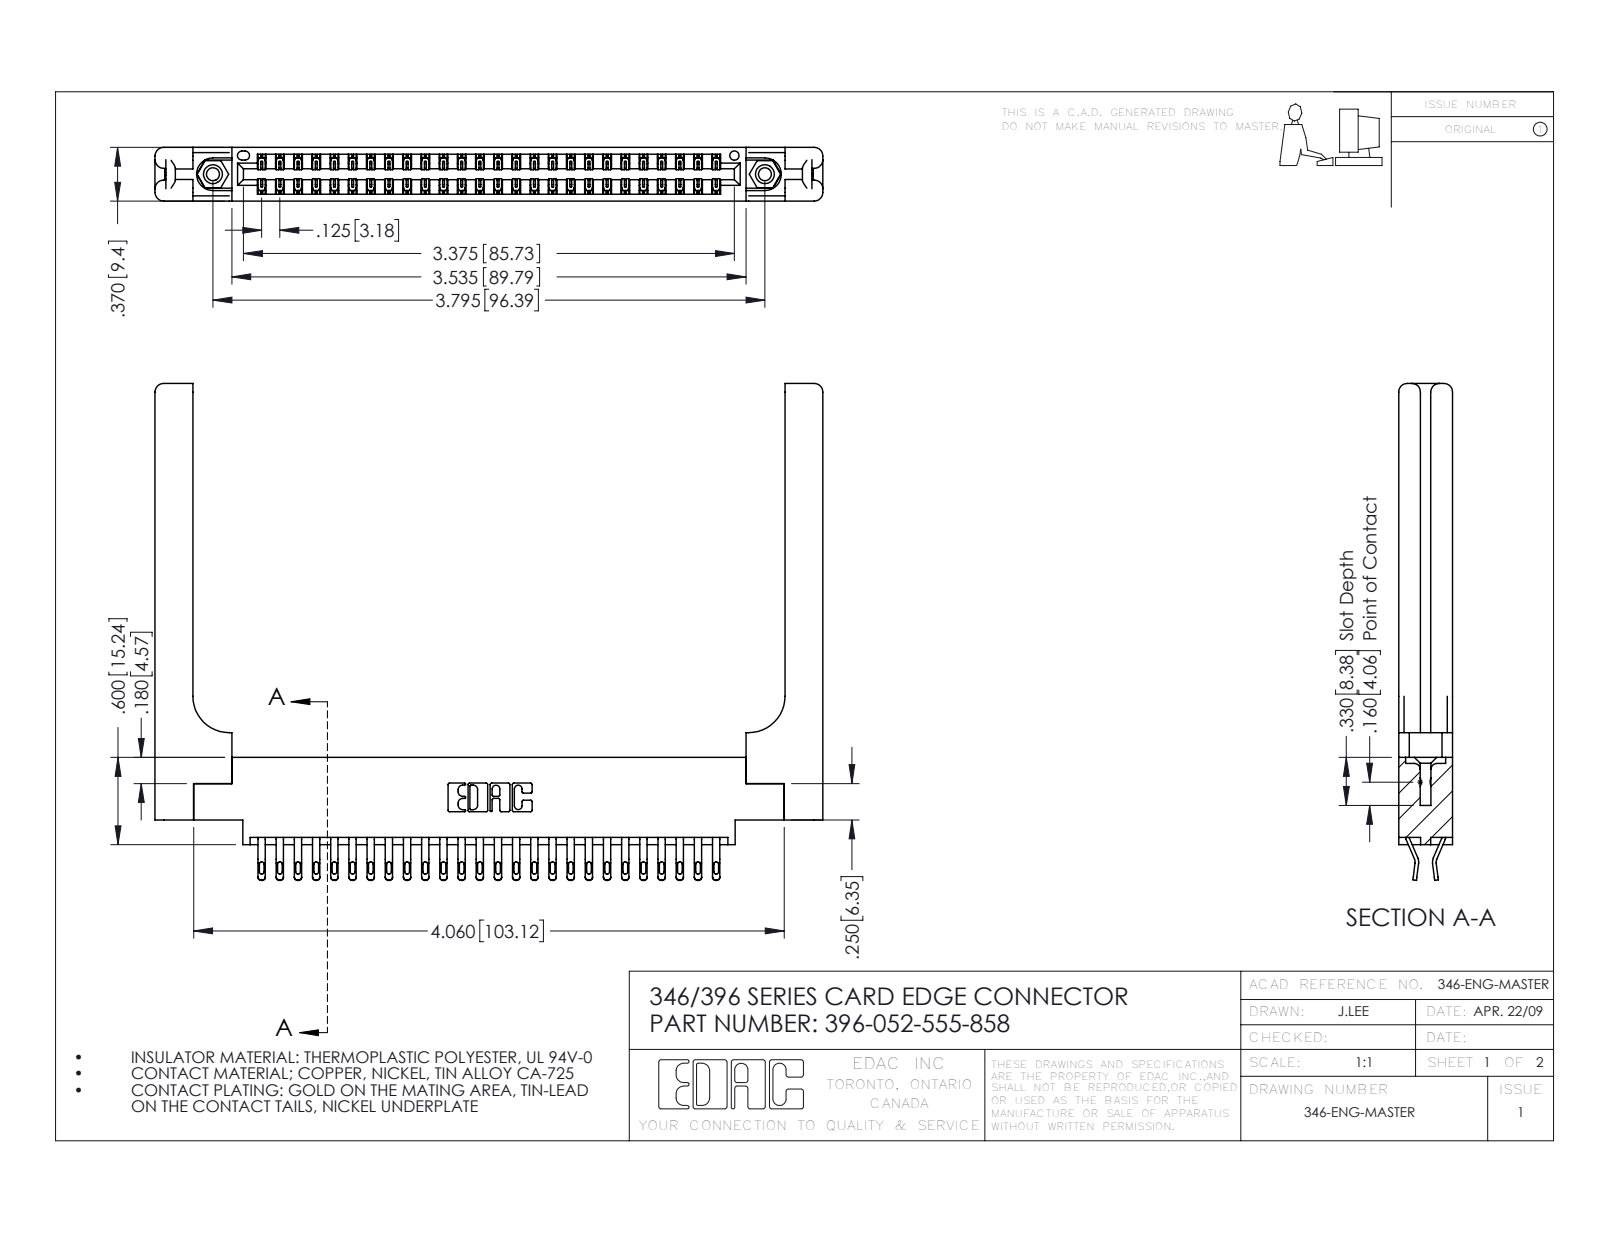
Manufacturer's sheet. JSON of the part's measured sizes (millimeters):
{"part_name": "345-292-001_555 Tail; 346-220-058_345-220-058; 396-052-555-858; 345-250-001_345-250-001-102 (+1 more)", "step_written_by": "SolidWorks 2016 (CONFIG_CONTROL_DESIGN)", "units": "millimeters", "bodies": {"solids": 57, "faces": 3398, "planar": 1944, "cylindrical": 1394, "other": 60}, "overall_size": [116.6, 86.7, 9.4], "volume_mm3": 18730, "surface_area_mm2": 20890, "round_holes": [[2.3, 2], [3.2, 2], [4, 2], [1.6, 1]], "round_bosses_or_shafts": [[3.9, 2]], "partial_cylinders_radius": [[0.4, 104], [0.5, 104], [0.2, 78], [0.3, 22], [1.5, 16], [0.2, 6], [0.8, 6], [0.7, 3]], "face_to_face_distances": [9.4, 1.8, 1.2, 8.2, 3.8, 3.8, 6.4, 0.6, 7.6, 7], "hole_center_spacings": [6.2, 91.1, 96.4]}
